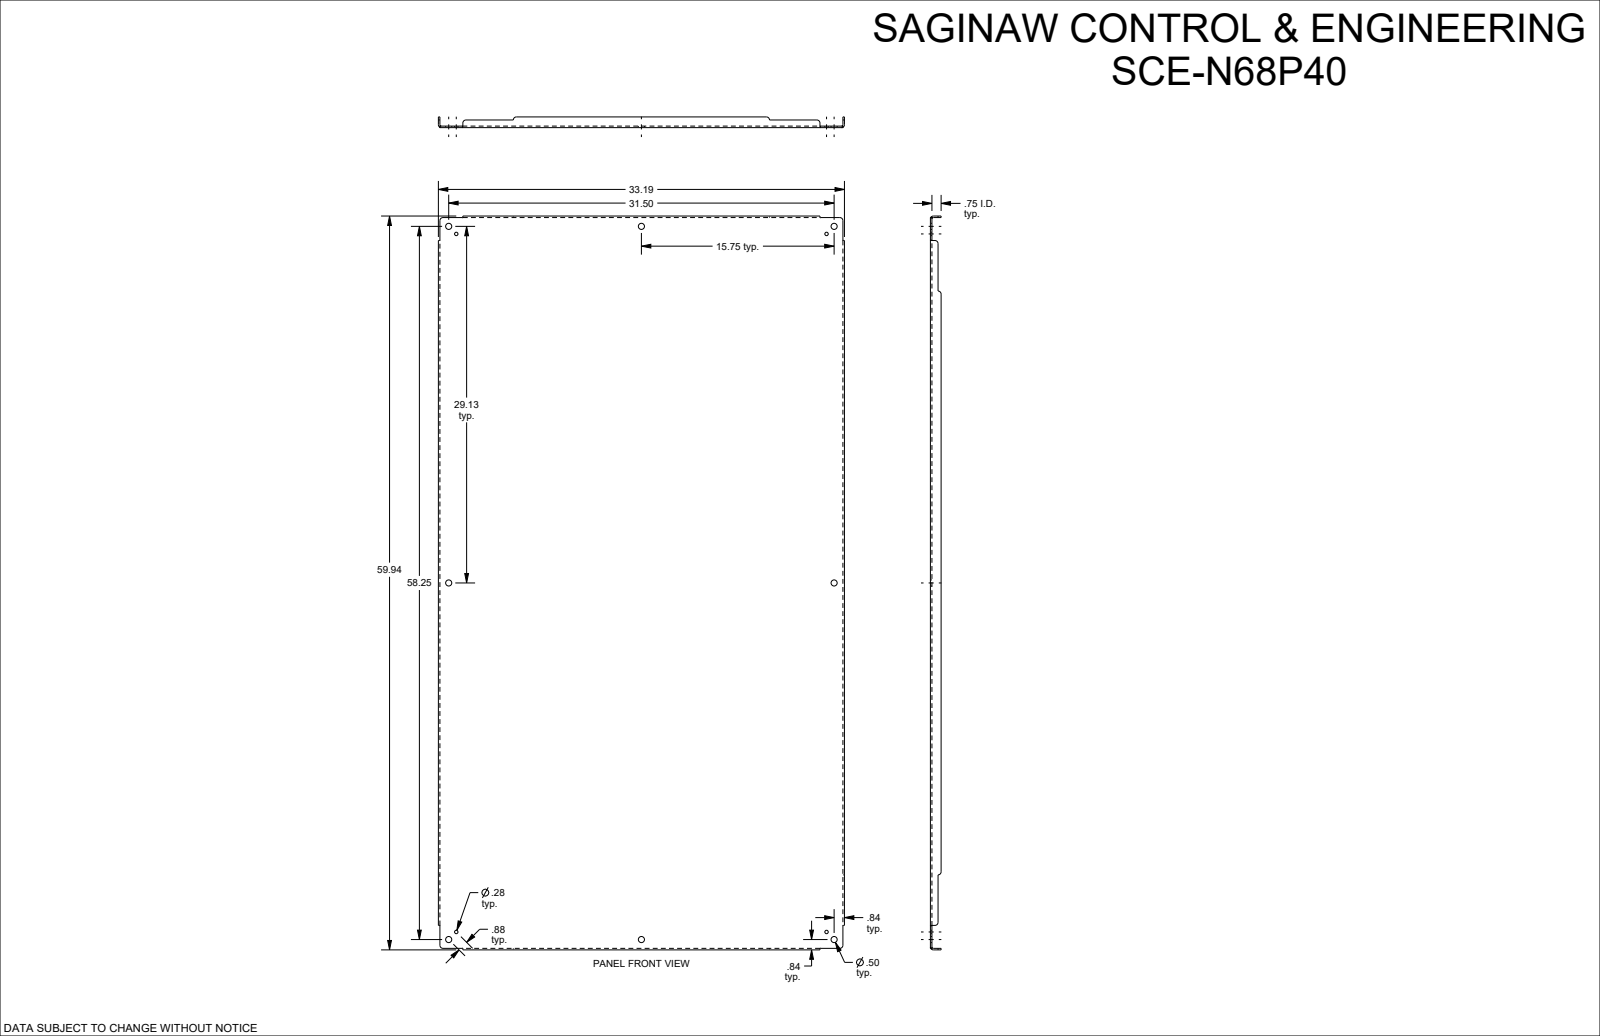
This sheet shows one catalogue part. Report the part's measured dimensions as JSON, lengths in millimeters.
{"part_name": "SCE-N68P40", "step_written_by": "SolidWorks 2023 (AUTOMOTIVE_DESIGN)", "units": "millimeters", "bodies": {"solids": 1, "faces": 122, "planar": 46, "cylindrical": 52, "other": 24}, "overall_size": [1522.4, 843, 22.2], "volume_mm3": 4285000, "surface_area_mm2": 2715000, "round_holes": [[12.7, 8], [7.1, 4]], "partial_cylinders_radius": [[6.4, 12], [2.8, 4], [6, 4]], "face_to_face_distances": [3.2, 839.8, 836.6, 842.9, 3.2, 1519.3, 19.1, 22.2, 1516, 1522.4], "hole_center_spacings": [22.2, 384.7, 400.1, 724.2, 739.8, 784.5, 841, 1067.5]}
